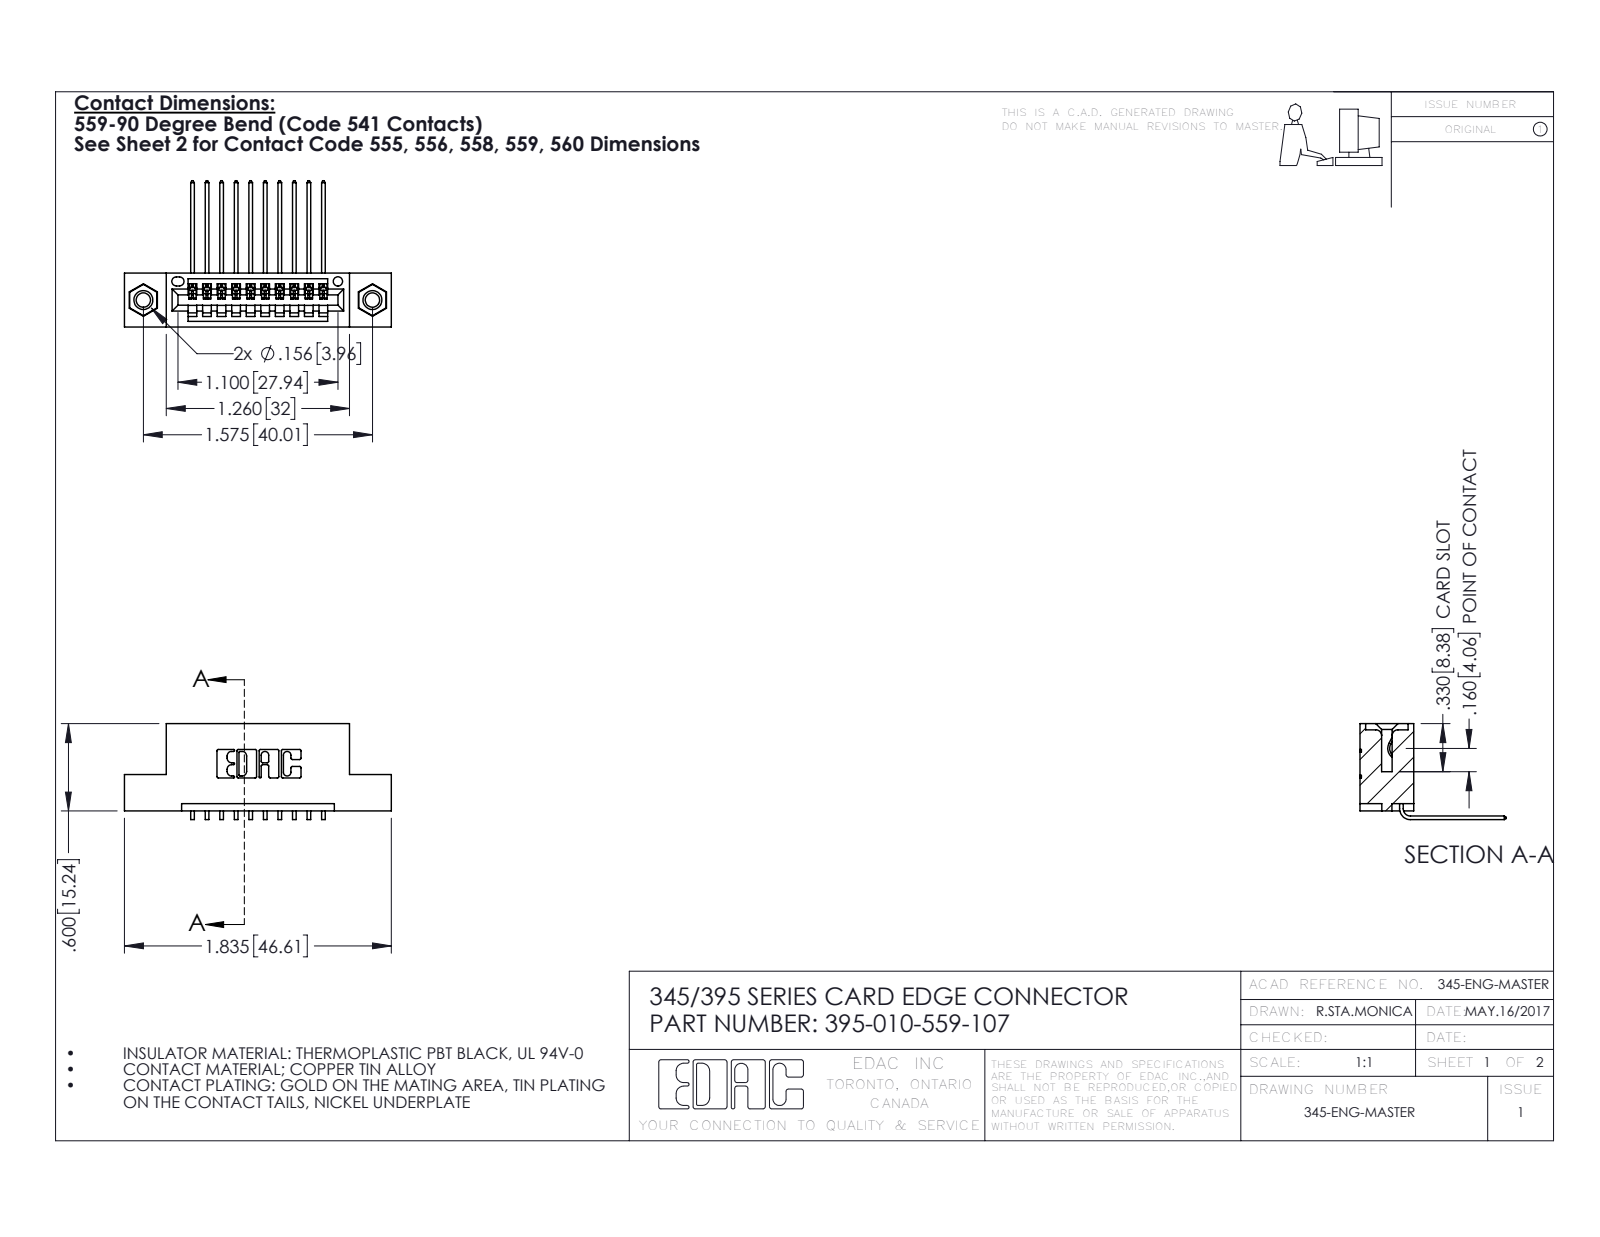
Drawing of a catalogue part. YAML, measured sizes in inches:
part_name: "345-250-001_345-250-005-103; 345 Part_Flush Mounting Lugs - 0.156 Dia-TI; 395-010-559-107; 345-292-001_558 559 Tail - 1"
step_written_by: "SolidWorks 2016 (CONFIG_CONTROL_DESIGN)"
units: inches
bodies: {solids: 13, faces: 786, planar: 532, cylindrical: 238, other: 16}
overall_size: [1.835, 1.005, 0.659]
volume: 0.255
surface_area: 8.299
round_holes:
  - {diameter: 0.098, count: 2}
  - {diameter: 0.125, count: 2}
  - {diameter: 0.156, count: 2}
  - {diameter: 0.064, count: 1}
round_bosses_or_shafts:
  - {diameter: 0.155, count: 2}
partial_cylinders:
  - {radius: 0.01, count: 22}
  - {radius: 0.006, count: 20}
  - {radius: 0.007, count: 6}
  - {radius: 0.031, count: 6}
  - {radius: 0.026, count: 3}
  - {radius: 0.031, count: 2}
  - {radius: 0.04, count: 2}
  - {radius: 0.014, count: 1}
face_to_face_distances: [0.2, 0.37, 0.072, 0.298, 0.1, 0.6, 0.098, 0.272, 0.025, 0.06]
hole_center_spacings: [0.27, 1.344, 1.575]
